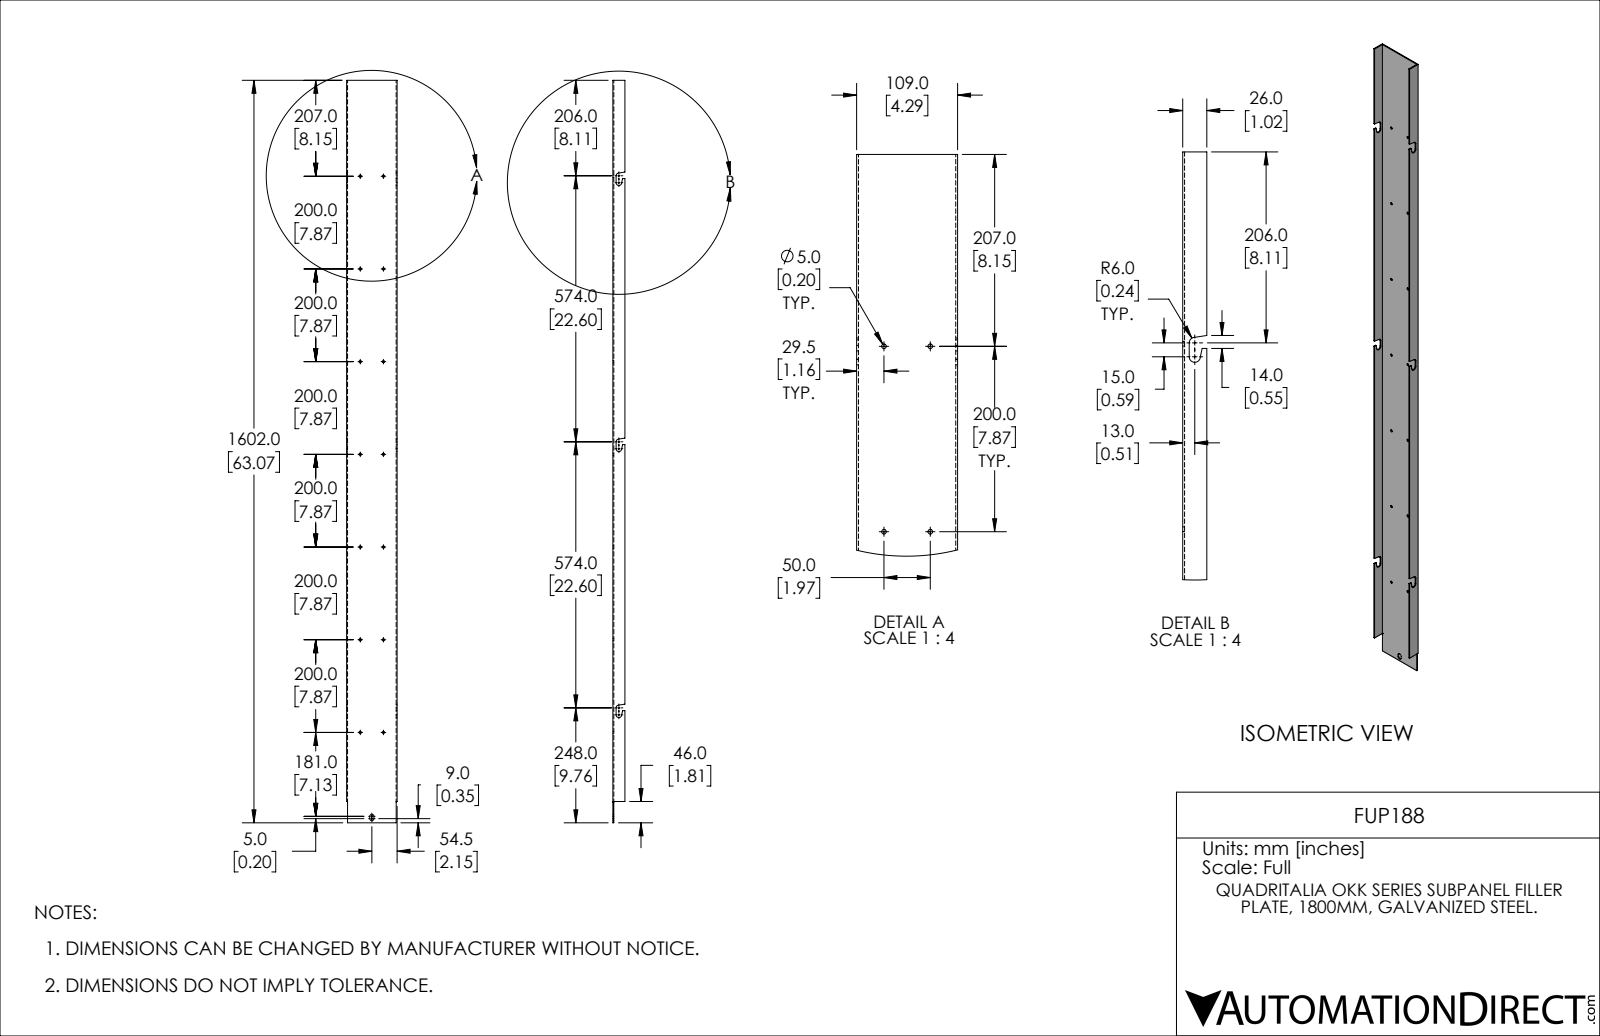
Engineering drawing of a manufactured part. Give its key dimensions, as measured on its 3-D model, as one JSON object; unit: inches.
{"part_name": "FUP188", "step_written_by": "SolidWorks 2021 (CONFIG_CONTROL_DESIGN)", "units": "inches", "bodies": {"solids": 1, "faces": 78, "planar": 50, "cylindrical": 28, "other": 0}, "overall_size": [63.071, 4.291, 1.024], "volume_in3": 30.06, "surface_area_in2": 776.3, "round_holes": [[0.197, 14]], "partial_cylinders_radius": [[0.236, 6], [0.177, 2]], "face_to_face_distances": [0.079, 4.213, 4.291, 4.134, 1.024, 0.945, 63.071, 0.276, 0.197, 0.748], "hole_center_spacings": [7.874, 8.117, 15.748, 15.87, 23.622, 23.704, 1.969, 31.496]}
